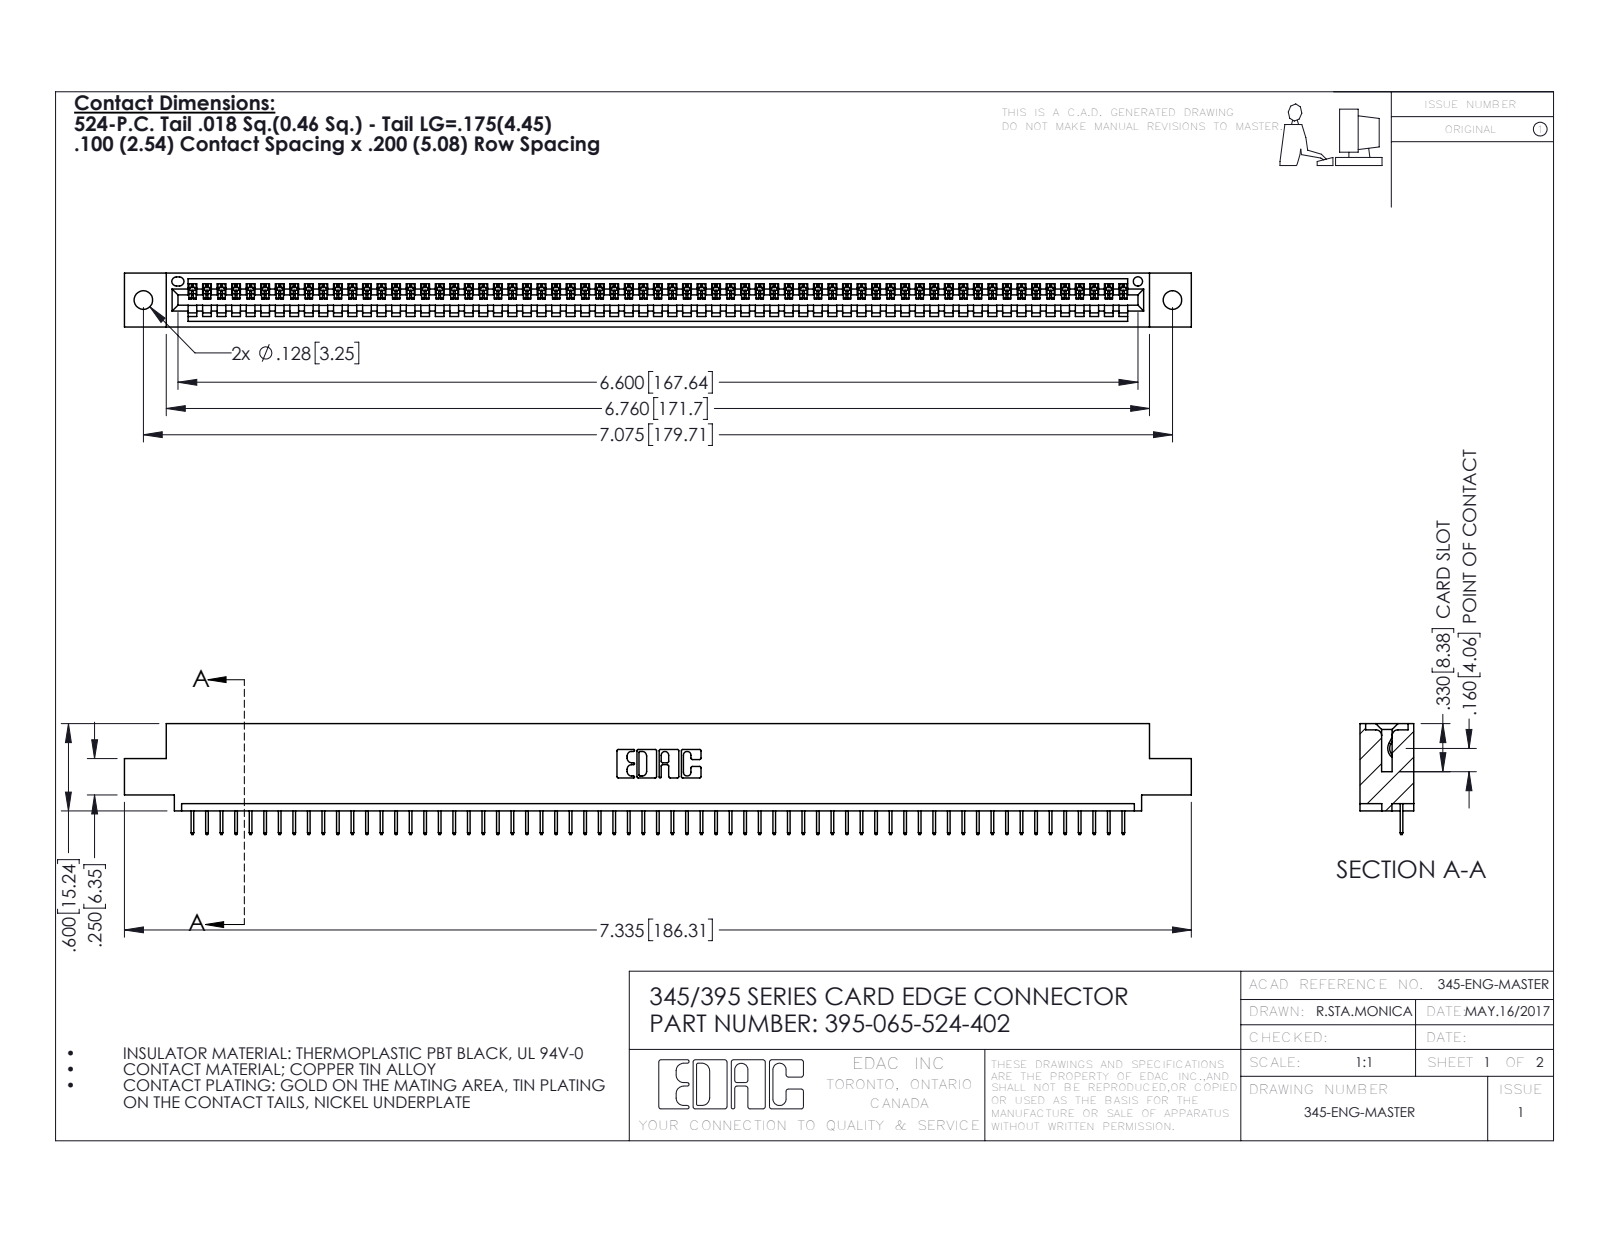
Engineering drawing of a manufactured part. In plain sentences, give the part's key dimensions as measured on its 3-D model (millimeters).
The part is named "395-065-524-402; 345 Part_0.110 Offset - 0.128 Dia; 345-292-001_345-293-124". Its 3-D file was written by "SolidWorks 2016 (CONFIG_CONTROL_DESIGN)". It is 66 solids with 4160 faces: 3074 planar, 1086 cylindrical and 0 other. Overall it measures 186.3 by 19.4 by 9.4 millimeters. Its volume is 17 520 cubic millimeters and its surface area 22 580 square millimeters. Round holes: 2 of diameter 3.3, 1 of diameter 1.6. Partial cylindrical surfaces (rounded edges, fillets, slot ends): 130 of radius 0.2, 22 of radius 0.3, 6 of radius 0.2, 6 of radius 0.8, 3 of radius 0.7, 2 of radius 0.8, 2 of radius 1, 1 of radius 0.4. The main face-to-face distances are 1.8, 7.6, 9.4, 5.1, 2.5, 6.9, 0.6, 5.7, 1.8, 3.8. The hole center spacings are 6.9, 173.7, 179.7.
